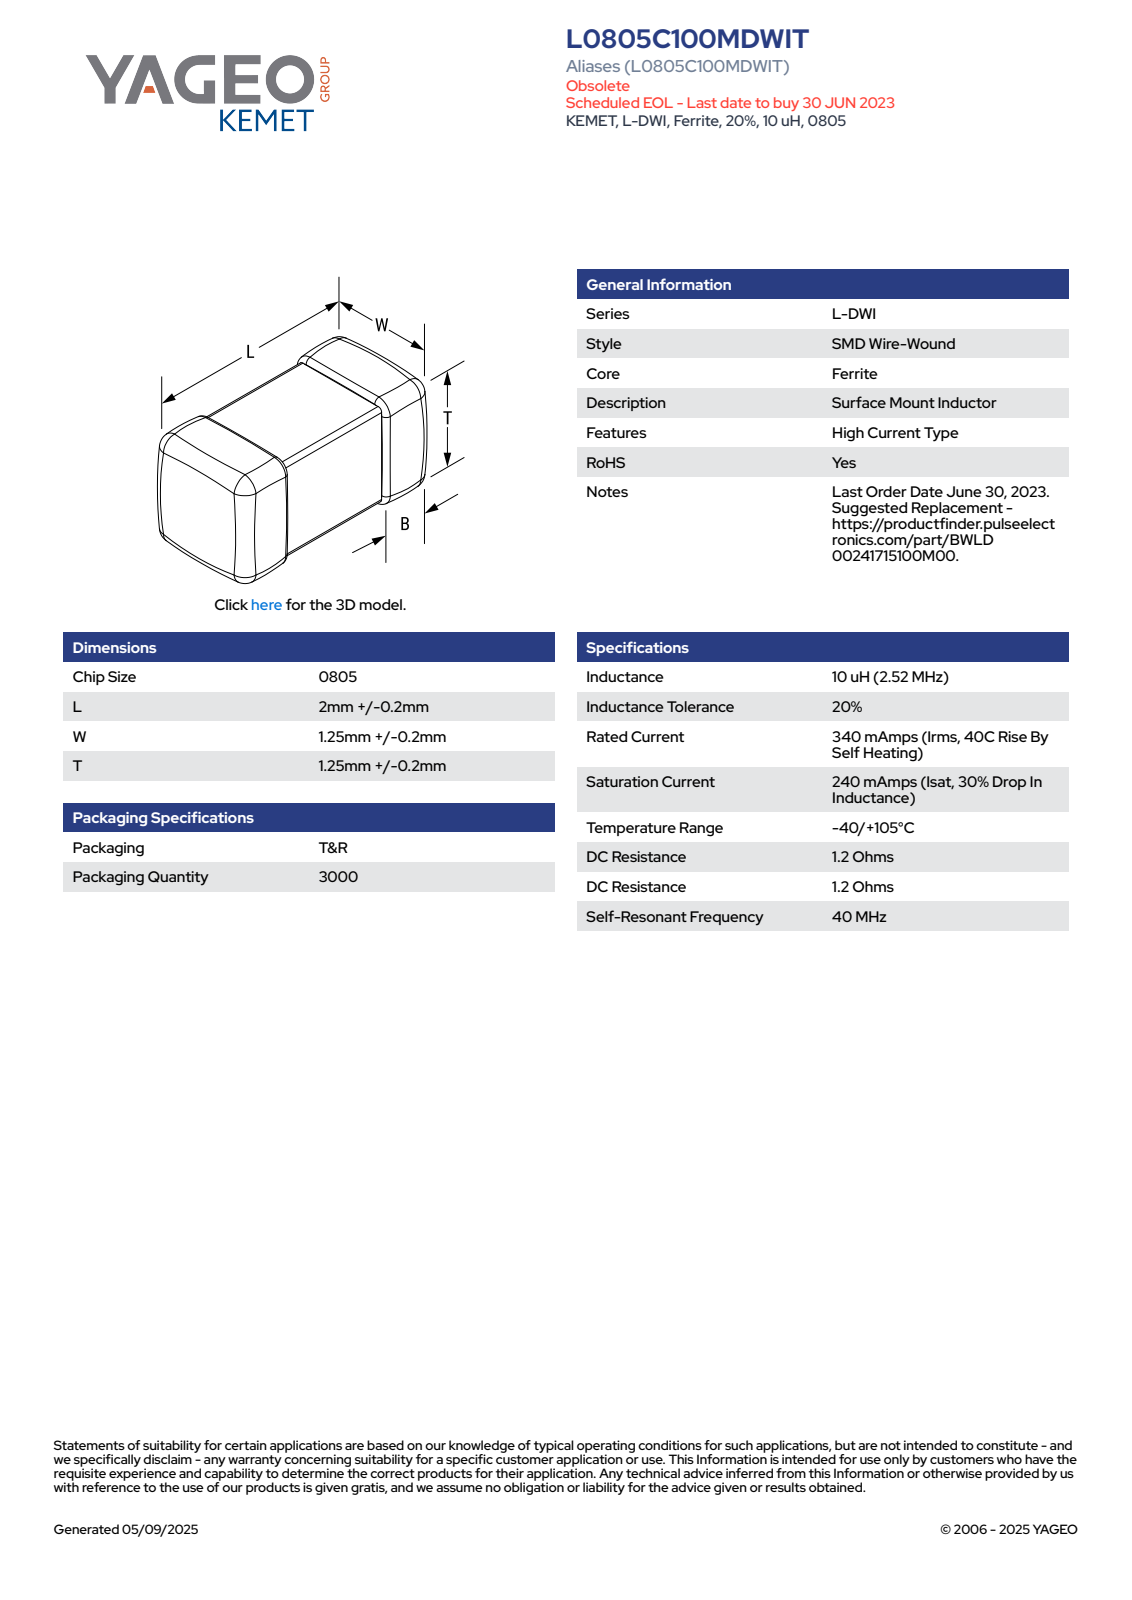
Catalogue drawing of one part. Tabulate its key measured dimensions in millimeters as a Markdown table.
| quantity | value |
| --- | --- |
| part name | IS_KC_0805_L2.2W1.45T1.45LL0.7 |
| STEP written by | SolidWorks 2014 (AUTOMOTIVE_DESIGN) |
| units | millimeters |
| bodies | 4 solids, 73 faces (73 planar, 0 cylindrical, 0 other) |
| overall size | 2.2 × 1.45 × 1.45 |
| volume | 5 mm³ |
| surface area | 17 mm² |
| main face-to-face distances | 1.43, 1.45, 1.41, 2.2, 0.7, 1.5, 0.8, 1, 1.2, 0.5 |
